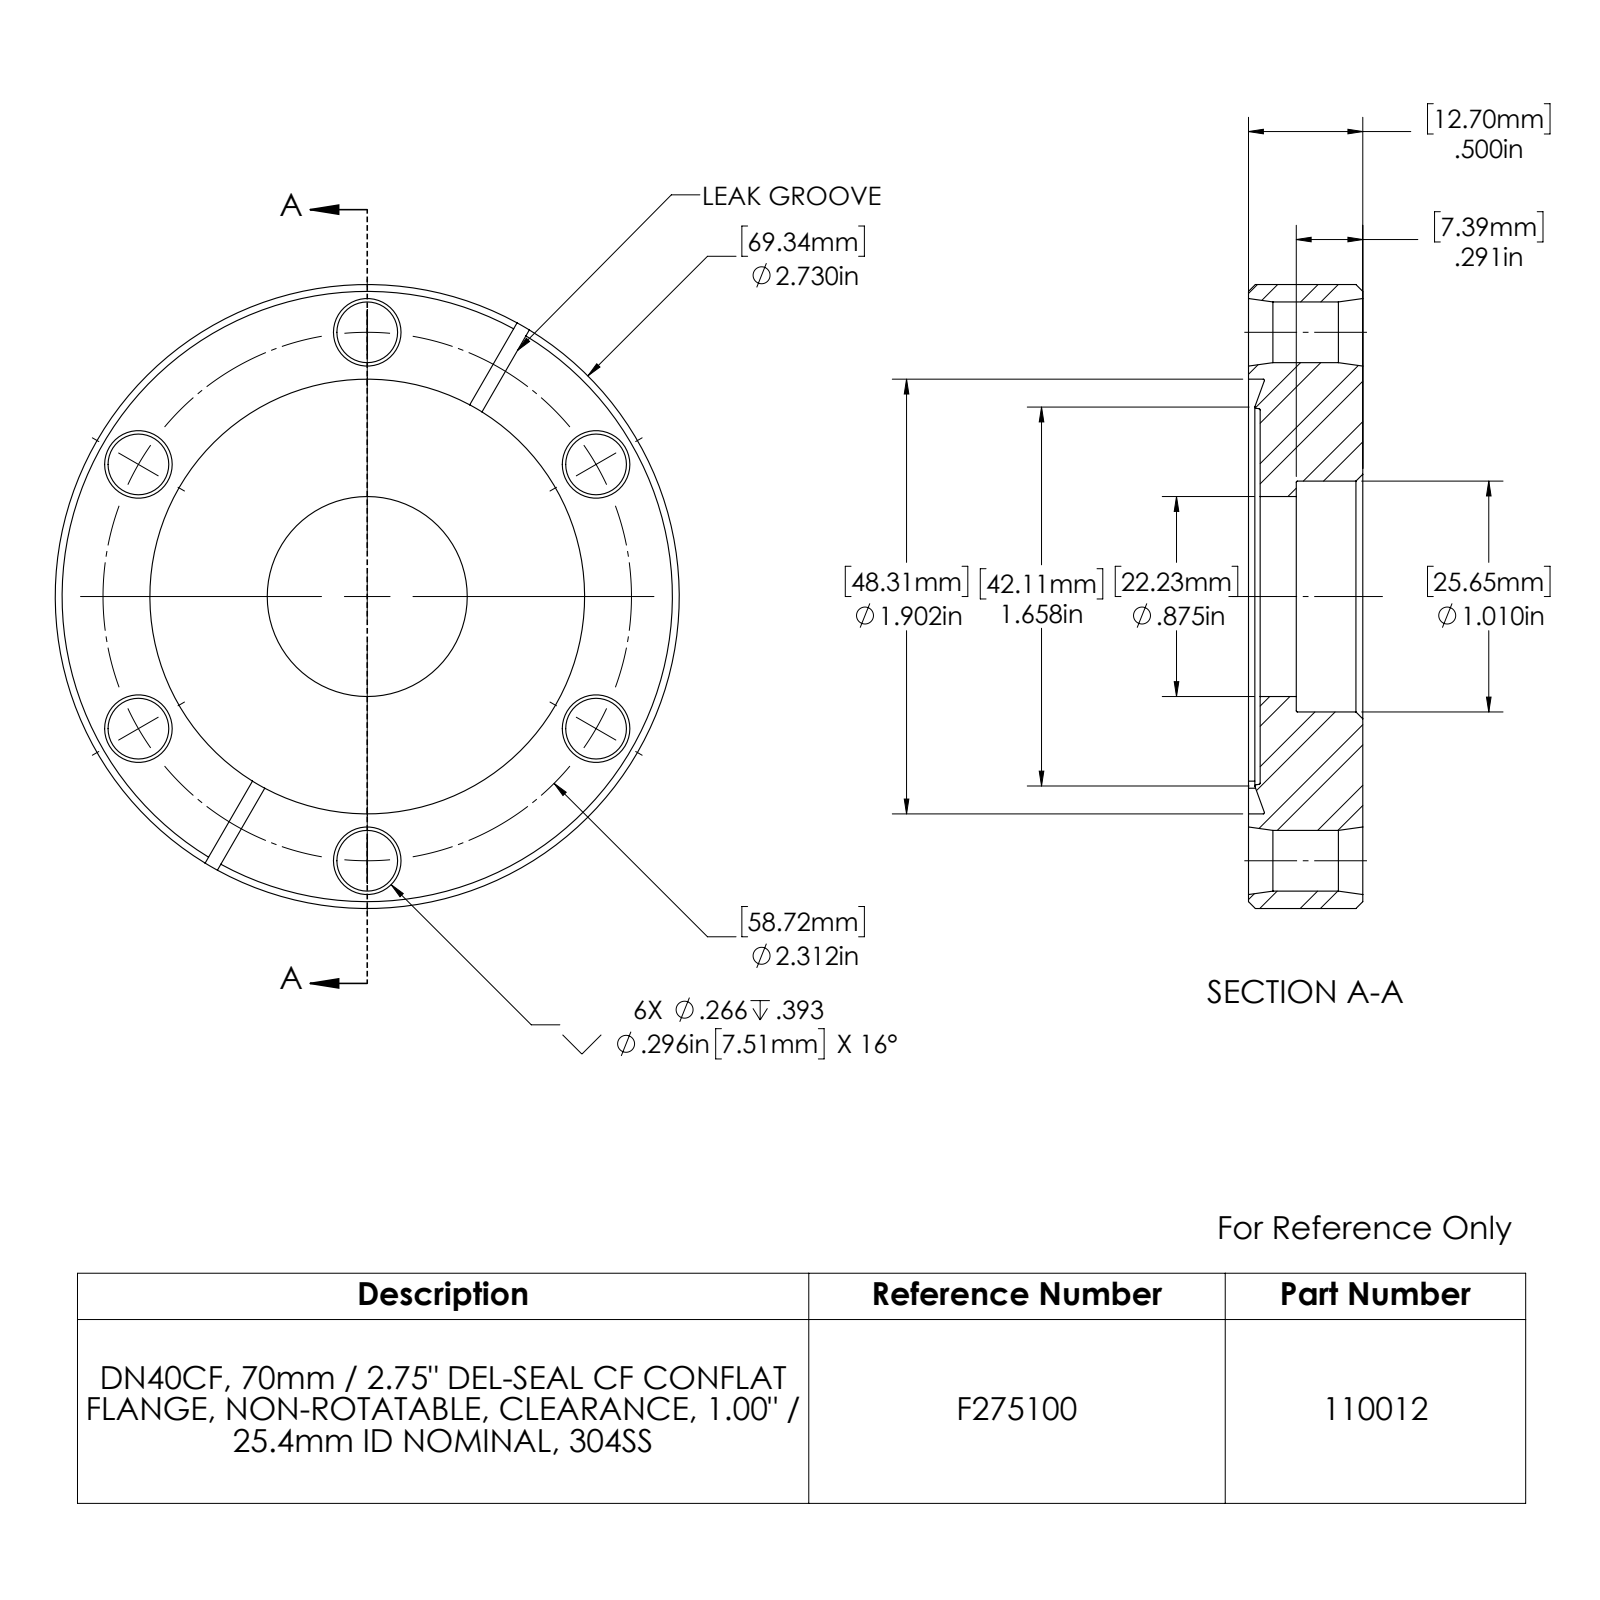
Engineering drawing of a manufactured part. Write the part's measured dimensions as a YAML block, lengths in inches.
part_name: "110012_A"
step_written_by: "SolidWorks 2022 (CONFIG_CONTROL_DESIGN)"
units: inches
bodies: {solids: 1, faces: 74, planar: 11, cylindrical: 20, other: 43}
overall_size: [2.73, 2.73, 0.5]
volume: 2.269
surface_area: 18.14
round_holes:
  - {diameter: 0.266, count: 6}
  - {diameter: 0.875, count: 1}
  - {diameter: 1.01, count: 1}
  - {diameter: 1.902, count: 1}
round_bosses_or_shafts:
  - {diameter: 2.73, count: 1}
face_to_face_distances: [0.5, 0.051, 0.449, 0.209, 0.158, 0.291, 0.052, 0.157, 0.448, 0.062]
hole_center_spacings: [1.156, 2.002, 2.002, 2.312, 2.312]
